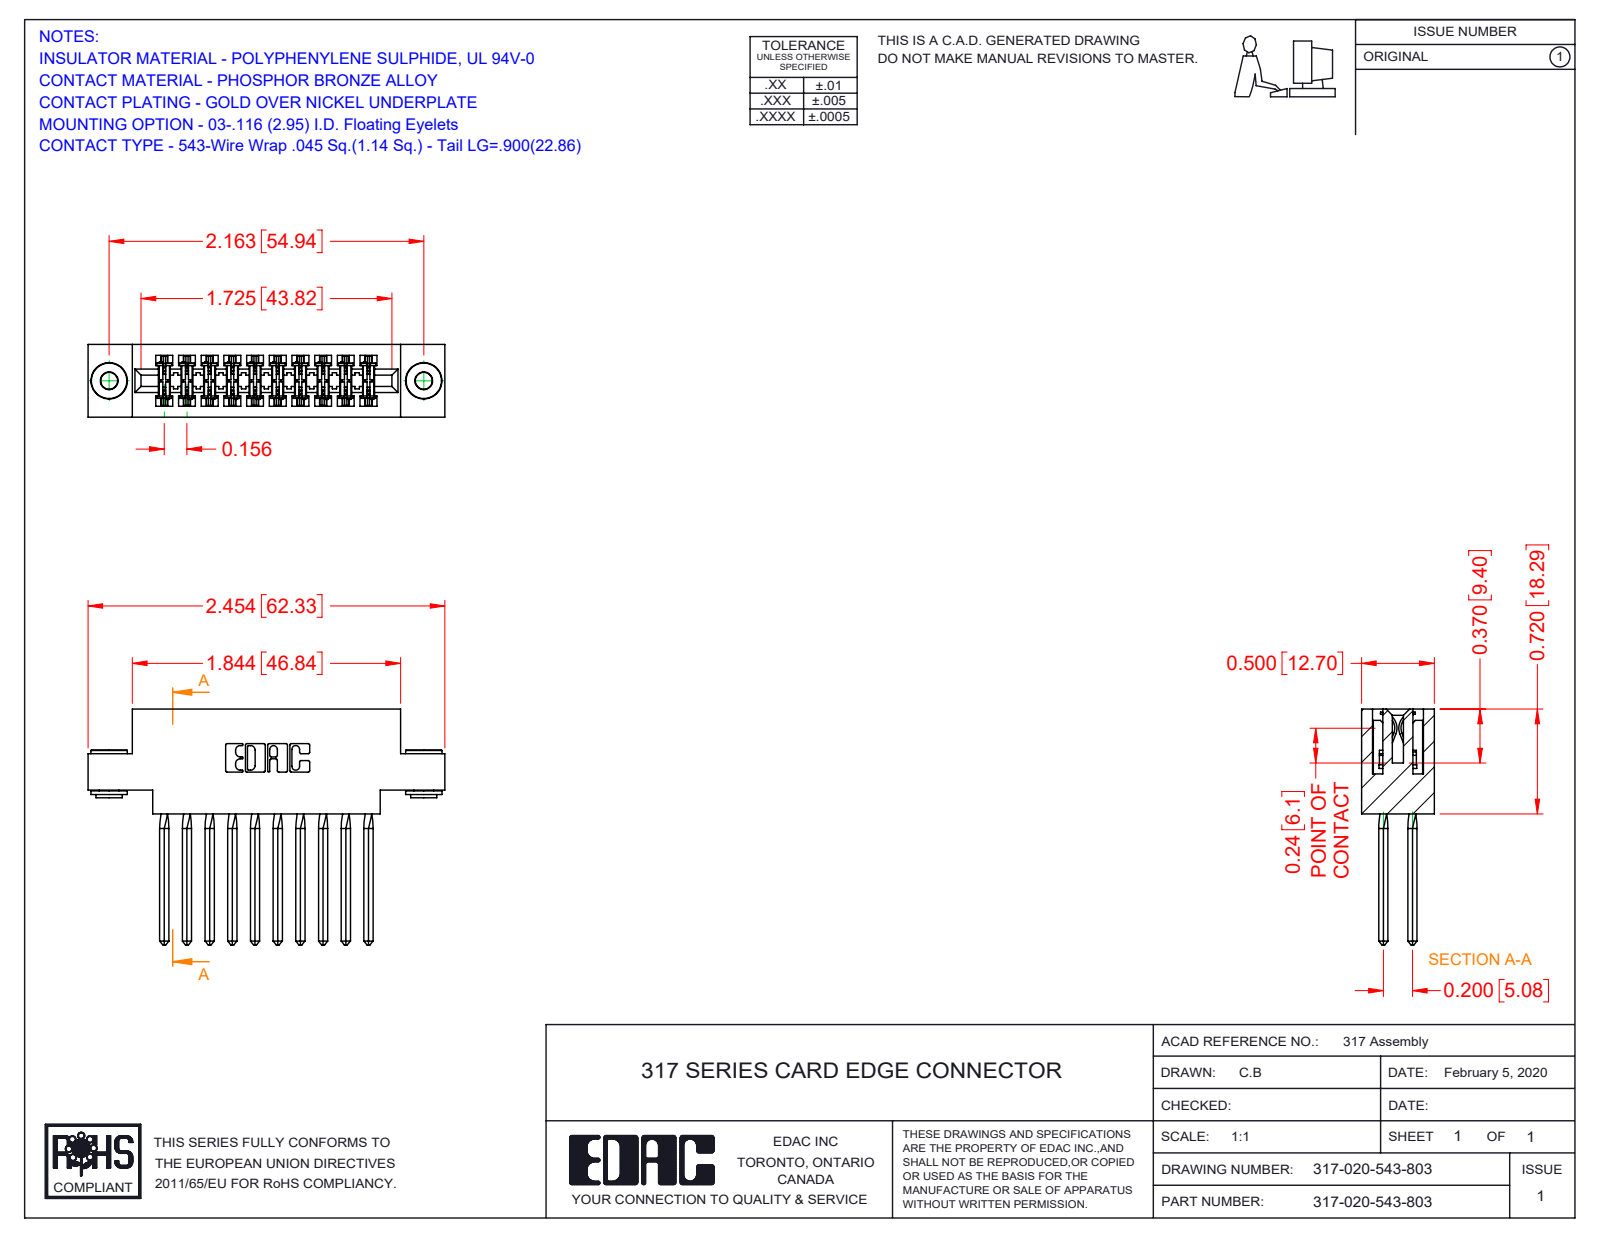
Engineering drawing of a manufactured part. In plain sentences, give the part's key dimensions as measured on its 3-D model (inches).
The part is named "317-290-001_543; 317 Part_.156 Dia - TH; 345-250-002_345-250-002-102; 317-020-543-803". Its 3-D file was written by "SolidWorks 2016 (CONFIG_CONTROL_DESIGN)". It is 23 solids with 1920 faces: 1528 planar, 304 cylindrical and 88 other. Overall it measures 2.454 by 1.62 by 0.5 inches. Its volume is 0.58 cubic inches and its surface area 20.72 square inches. Round holes: 2 of diameter 0.116, 2 of diameter 0.156. Round bosses or shafts: 2 of diameter 0.25, 2 of diameter 0.18, 2 of diameter 0.136. Partial cylindrical surfaces (rounded edges, fillets, slot ends): 40 of radius 0.015, 22 of radius 0.01, 6 of radius 0.007, 6 of radius 0.031, 3 of radius 0.026, 2 of radius 0.095, 2 of radius 0.1, 2 of radius 0.11. The main face-to-face distances are 0.5, 0.11, 0.075, 0.425, 0.22, 0.331, 0.35, 0.156, 0.305, 0.116. The hole center spacings are 2.163.
